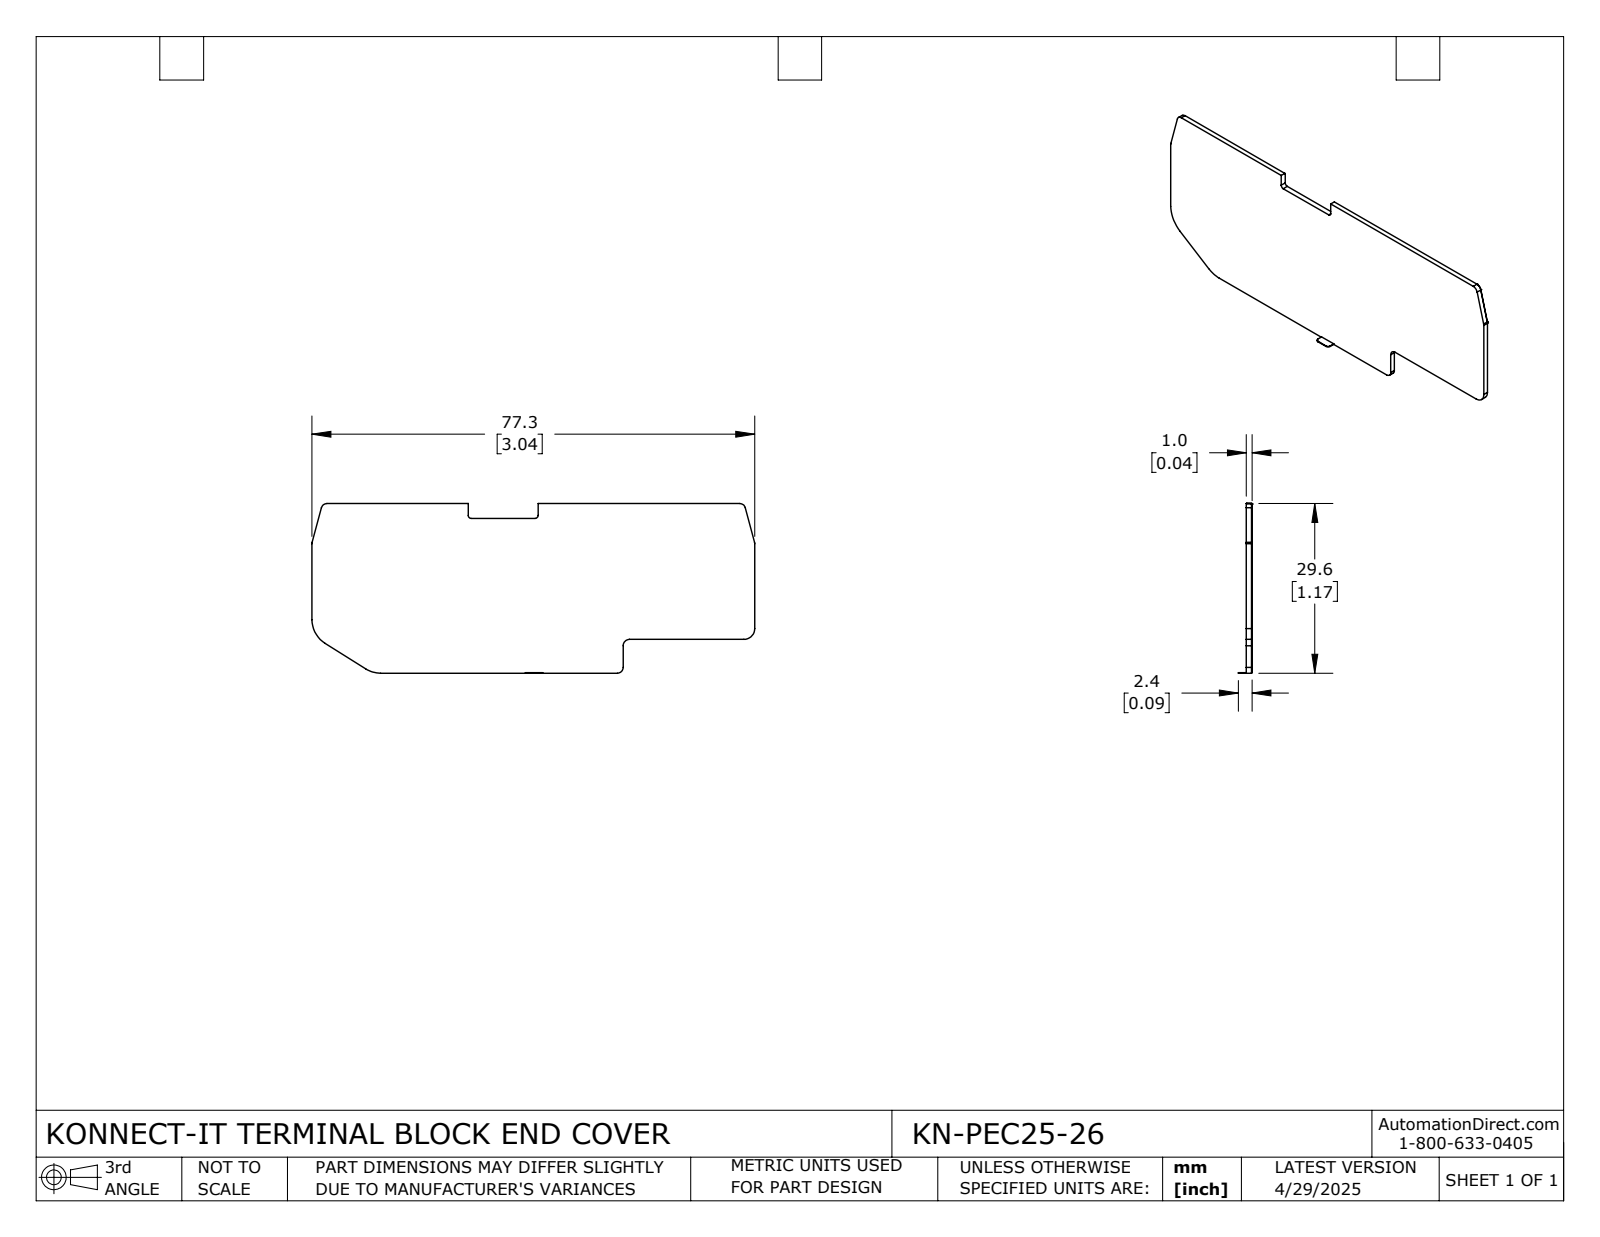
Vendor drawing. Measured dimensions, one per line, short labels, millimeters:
name: KN-PEC25-26
written by: SolidWorks 2024 (CONFIG_CONTROL_DESIGN)
unit: mm
bodies: 1 solid, 52 faces (30 planar, 22 cylindrical, 0 other)
size: 77.31 × 29.61 × 2.4
volume: 2 071 mm³; area: 4 361 mm²
rounds: 5× R0.9, 5× R1, 4× R0.5, 2× R4.8, 2× R4.9, 1× R1.1, 1× R1.2, 1× R1.8
face distances: 1, 29.61, 5.9, 0.9, 23.71, 29.51, 77.31, 27.02, 21.12, 2.59
